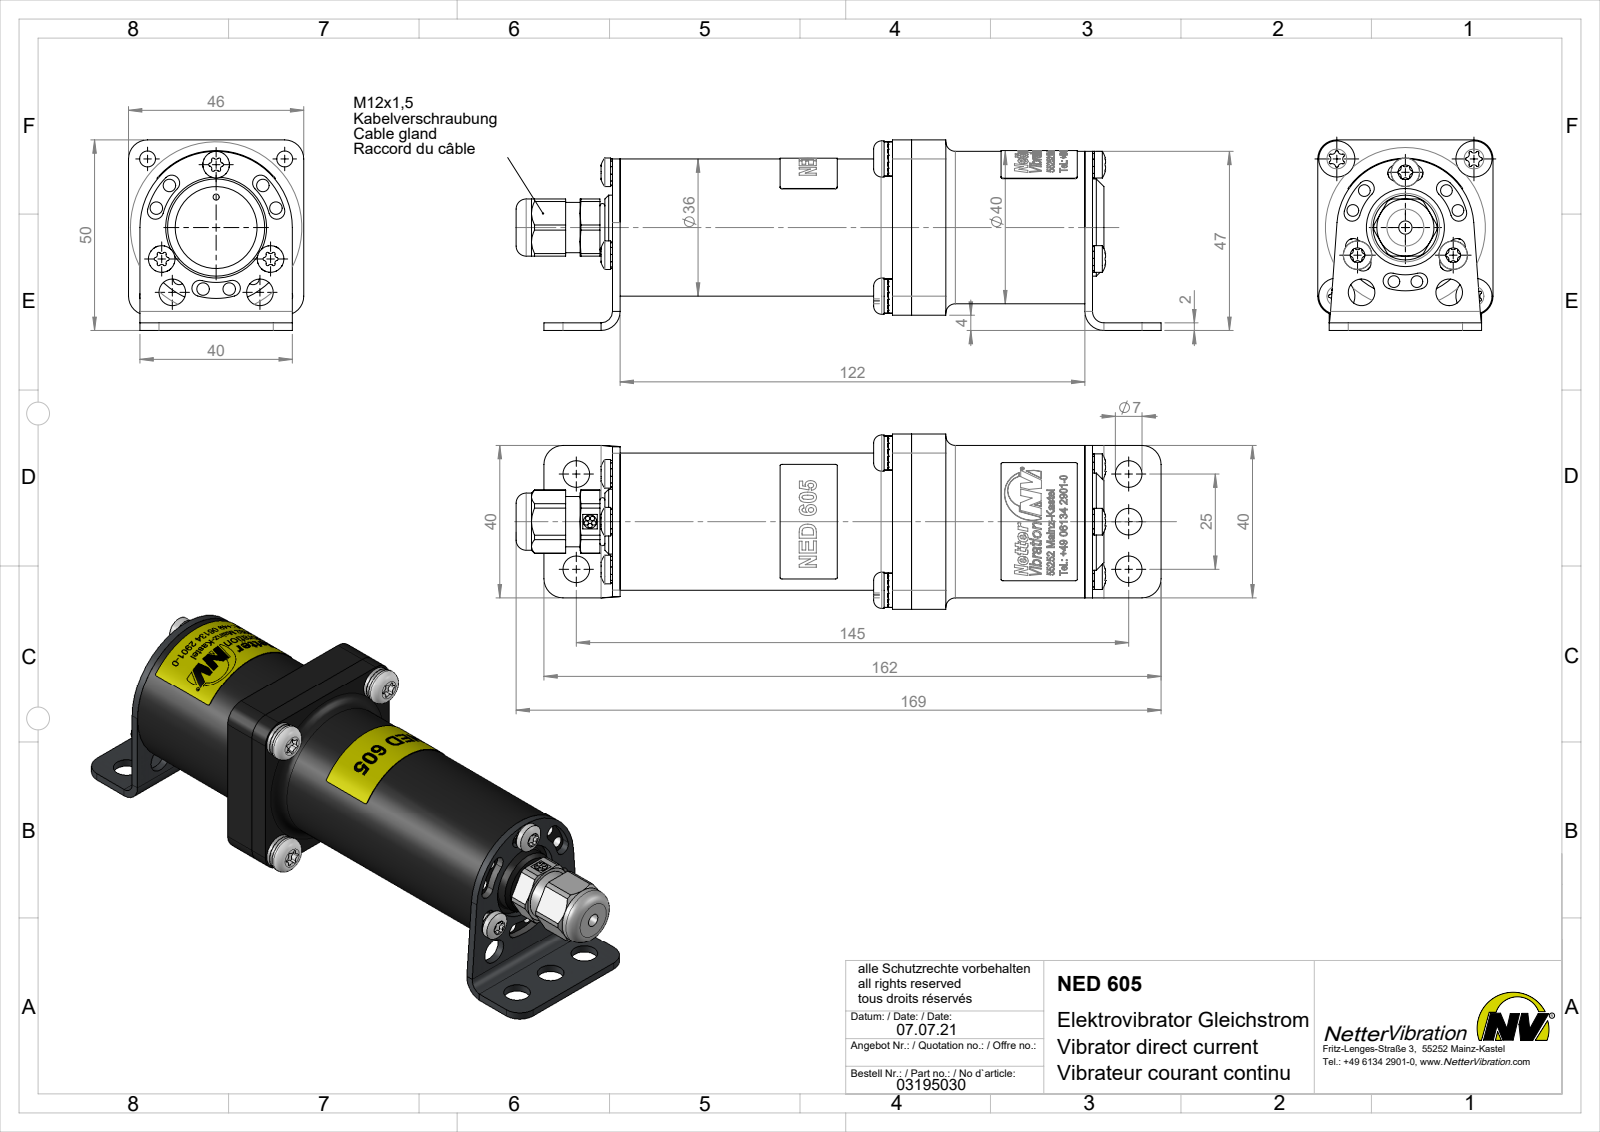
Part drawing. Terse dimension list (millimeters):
name: NED 605 #03195030
written by: SolidWorks 2015 (AUTOMOTIVE_DESIGN)
unit: mm
bodies: 41 solids, 3158 faces (2097 planar, 694 cylindrical, 367 other)
size: 169.3 × 50 × 46
volume: 77 609 mm³; area: 57 816 mm²
holes: 15× ⌀3.1, 15× ⌀3.3, 8× ⌀7, 6× ⌀4.3, 5× ⌀1.16, 4× ⌀4.2, 4× ⌀5.2, 4× ⌀5.4, 3× ⌀0.8, 2× ⌀1.6, 1× ⌀3.5, 1× ⌀10.5
bosses: 6× ⌀7, 4× ⌀9.5, 4× ⌀9, 4× ⌀5, 3× ⌀7.5, 3× ⌀4, 3× ⌀3.9, 1× ⌀40
rounds: 36× R0.39, 36× R0.69, 24× R0.33, 24× R0.95, 24× R2.1, 10× R5, 8× R0.5, 2× R3
face distances: 2, 5, 124, 50.5, 45.5, 76.5, 71.5, 122, 46, 73.5
hole spacings: 16.5, 32.82, 6.86, 13.42, 18.29, 26.86, 12.74, 29.49
